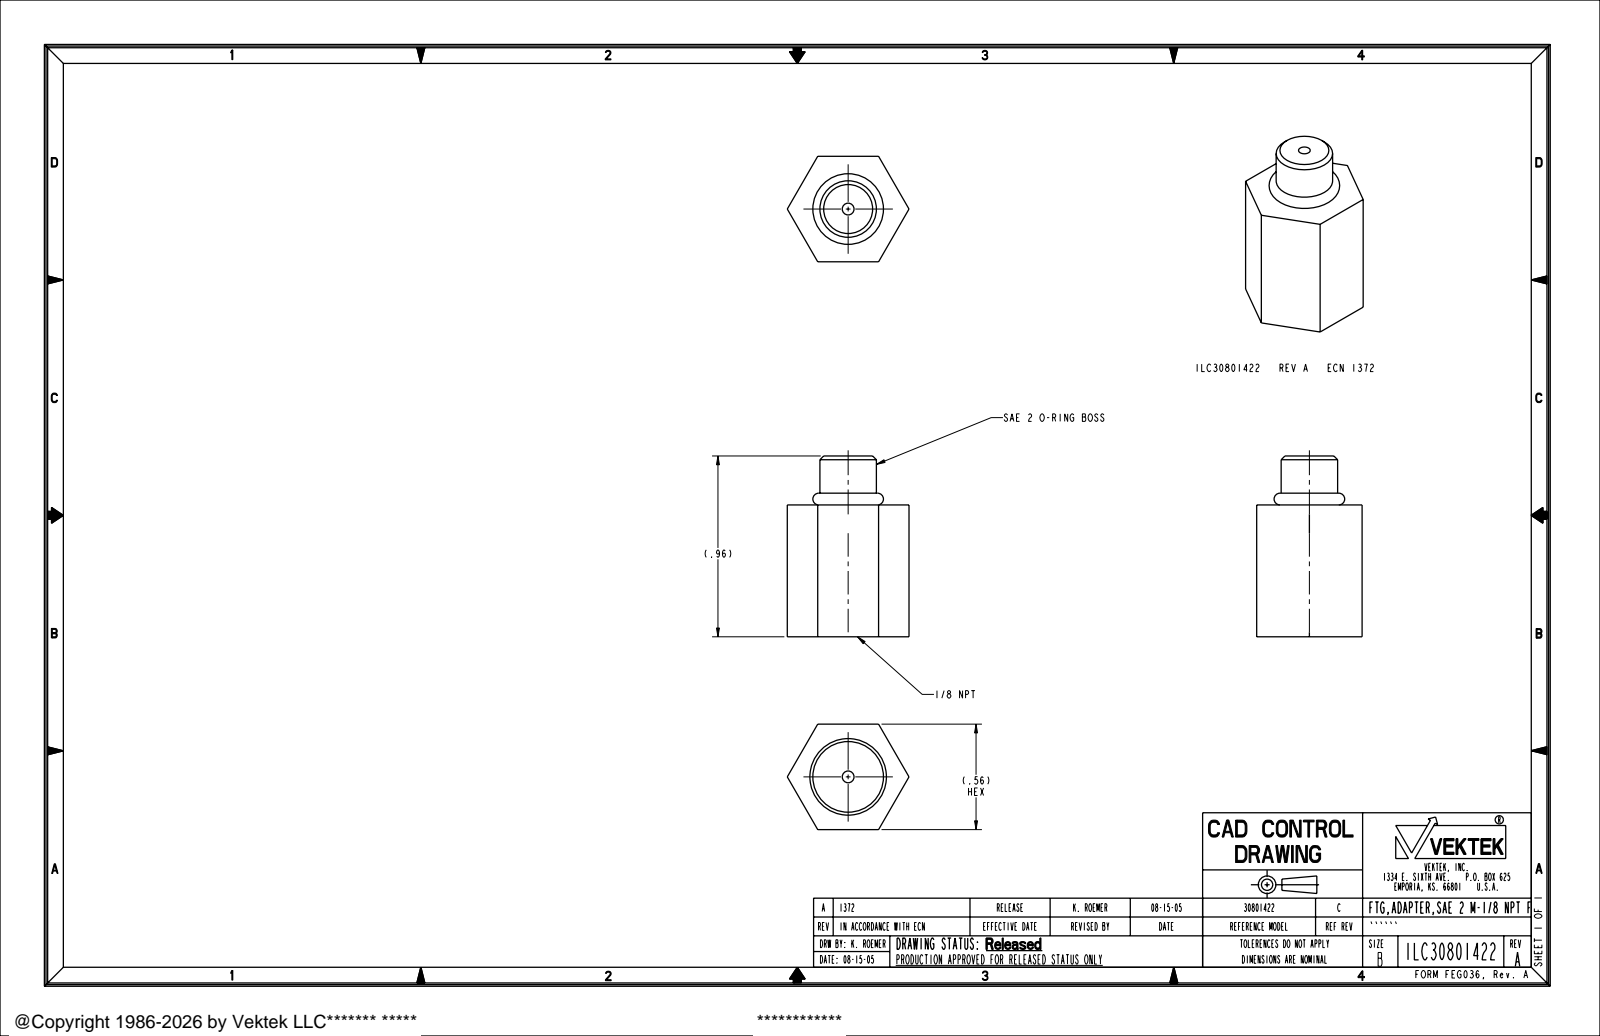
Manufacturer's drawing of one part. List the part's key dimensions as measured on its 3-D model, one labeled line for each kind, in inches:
Part name (STEP PRODUCT): ILC30801422
STEP written by: PRO/ENGINEER BY PARAMETRIC TECHNOLOGY CORPORATION, 2004290 (AUTOMOTIVE_DESIGN_CC2)
Units: inches
Bodies: 1 solid, 24 faces (10 planar, 8 cylindrical, 6 other)
Overall size (bounding box): 0.96 × 0.647 × 0.56
Volume: 0.153 in³ · Surface area: 2.857 in²
Round holes (diameter × count): ⌀0.063 ×1, ⌀0.375 ×1
Round bosses / shafts (diameter × count): ⌀0.3 ×1
Main face-to-face distances: 0.56, 0.7, 0.5, 0.2, 0.96, 0.46, 0.26
